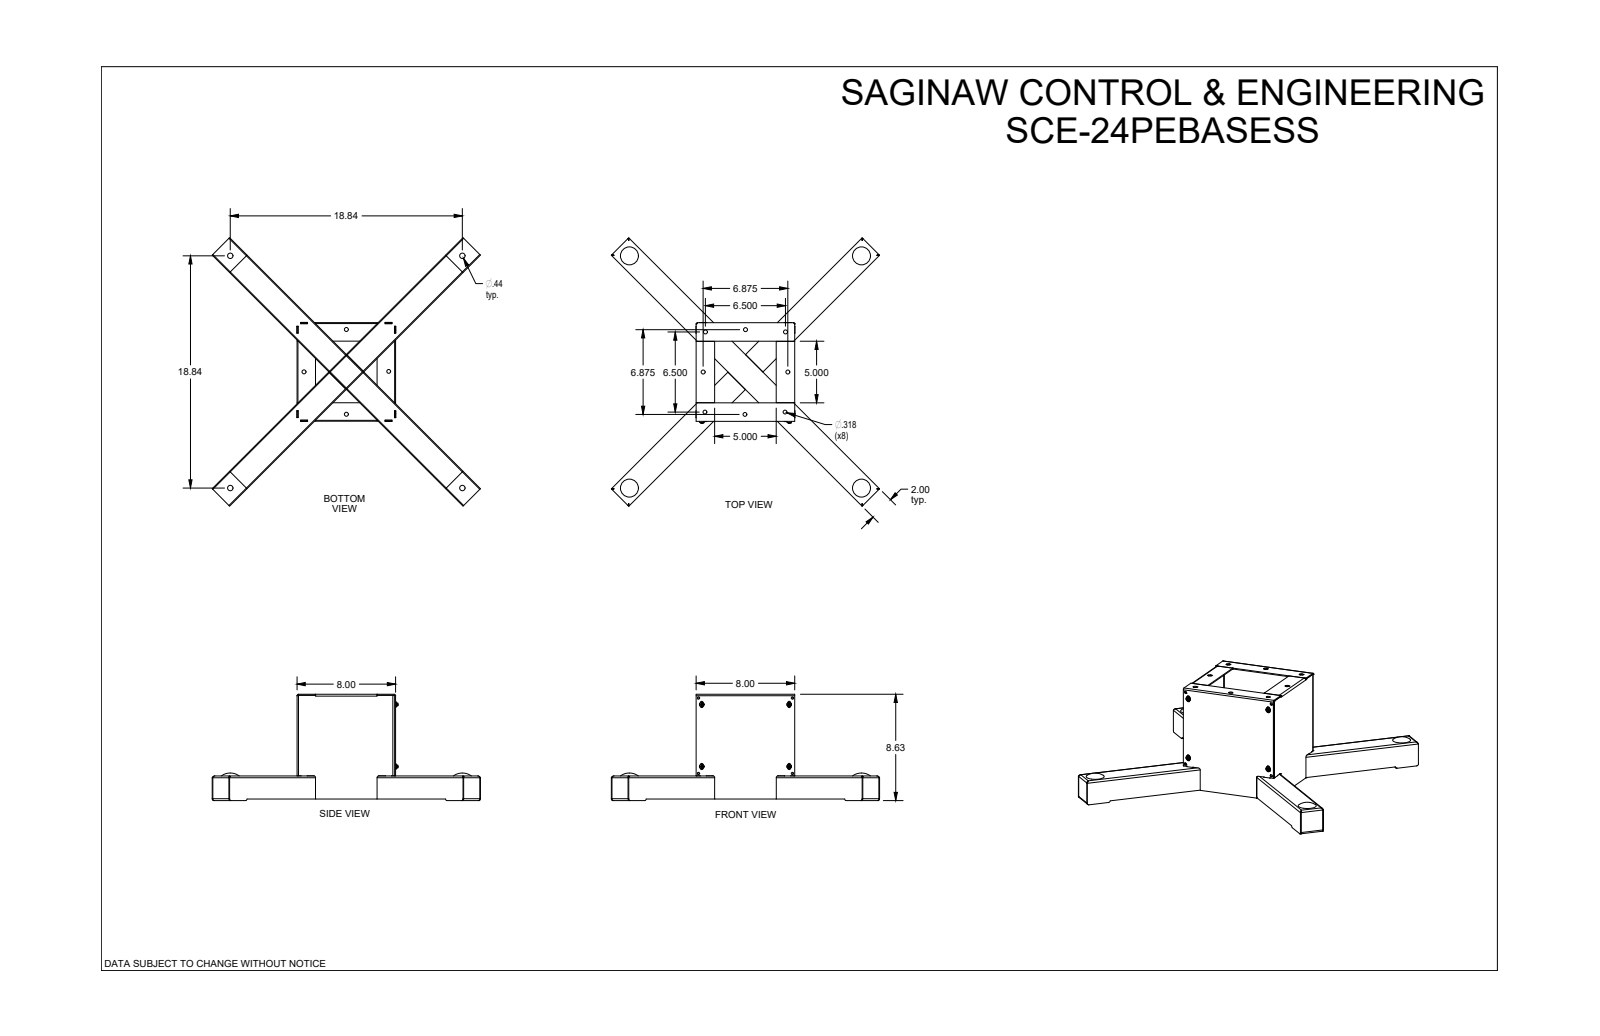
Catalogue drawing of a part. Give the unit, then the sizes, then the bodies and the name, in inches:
Units: inches
Overall size (bounding box): 21.68 × 21.68 × 8.625
Round holes (diameter × count): ⌀0.32 ×7, ⌀0.19 ×4, ⌀0.438 ×4, ⌀0.971 ×4
Round bosses / shafts (diameter × count): ⌀1.14 ×4, ⌀0.86 ×4, ⌀0.34 ×4, ⌀0.249 ×4
Partial cylindrical surfaces — rounded edges, fillets, slot ends (radius × count): R0.042 ×35, R0.117 ×35, R0.042 ×12, R0.117 ×12, R0.031 ×2
Main face-to-face distances: 0.075, 7.917, 0.075, 1.925, 7.992, 7.842, 1.85, 1.924, 2, 6.625
Hole centre spacings: 3.25, 7.267, 6.5, 18.841, 4.596, 5, 7.1, 8.684
Volume: 48.19 in³ · Surface area: 1 275 in²
Bodies: 11 solids, 359 faces (112 planar, 159 cylindrical, 88 other)
Part name (STEP PRODUCT): SCE-24PEBASE_REV2
STEP written by: SolidWorks 2021 (AUTOMOTIVE_DESIGN)
